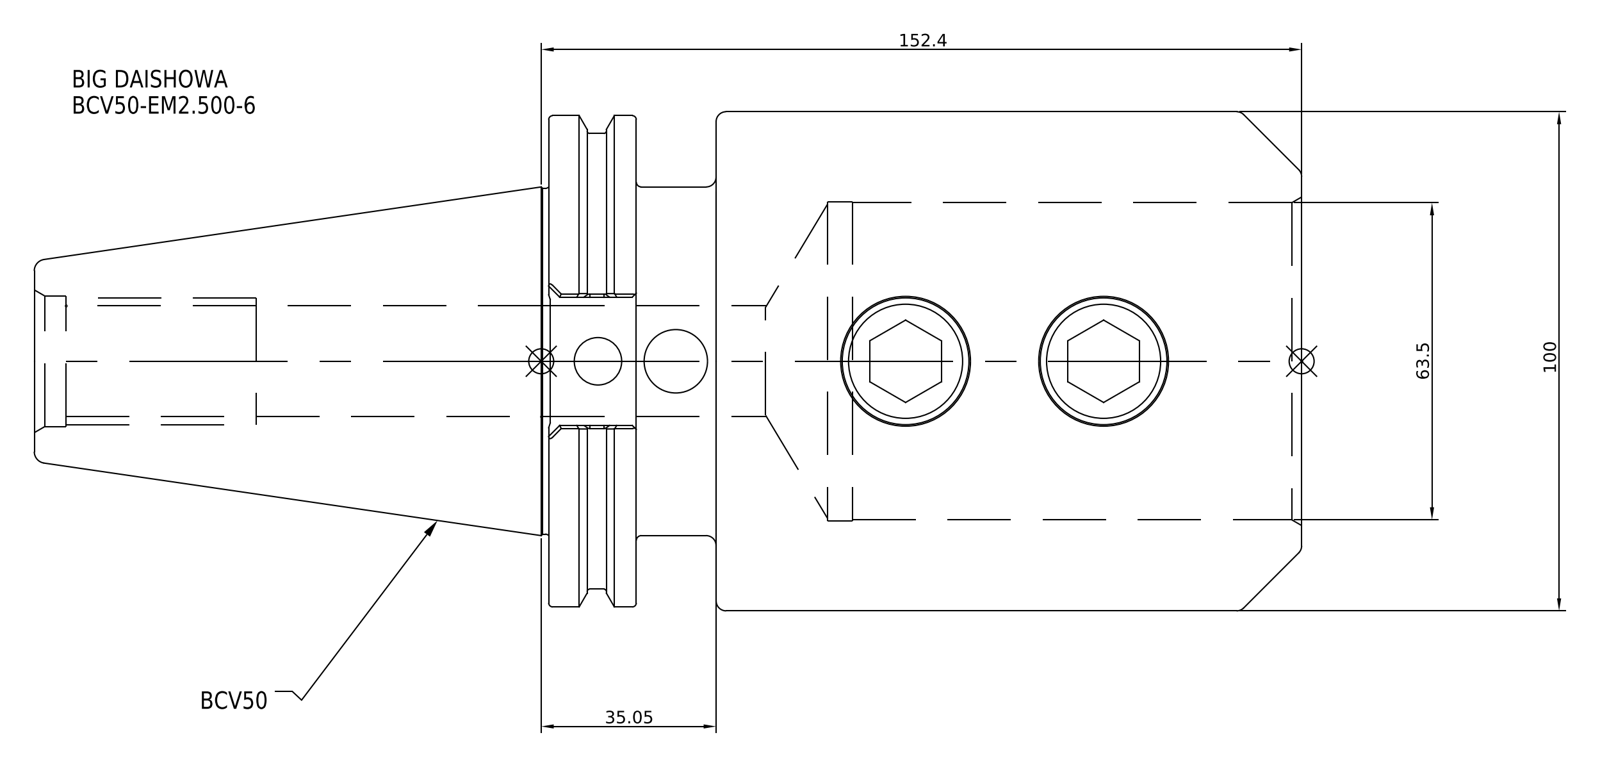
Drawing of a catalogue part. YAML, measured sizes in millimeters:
part_name: "BCV50-EM2_500-6"
step_written_by: "SolidWorks 2021 (CONFIG_CONTROL_DESIGN)"
units: millimeters
bodies: {solids: 1, faces: 30, planar: 8, cylindrical: 14, other: 8}
overall_size: [254, 100, 100]
volume: 971221
surface_area: 106866
round_holes:
  - {diameter: 63.5, count: 1}
round_bosses_or_shafts:
  - {diameter: 100, count: 1}
  - {diameter: 98.43, count: 1}
  - {diameter: 91.29, count: 1}
  - {diameter: 69.85, count: 1}
face_to_face_distances: [33.55, 16, 17.55, 117.35, 133.35, 150.9, 254, 136.65, 120.65, 103.1]
